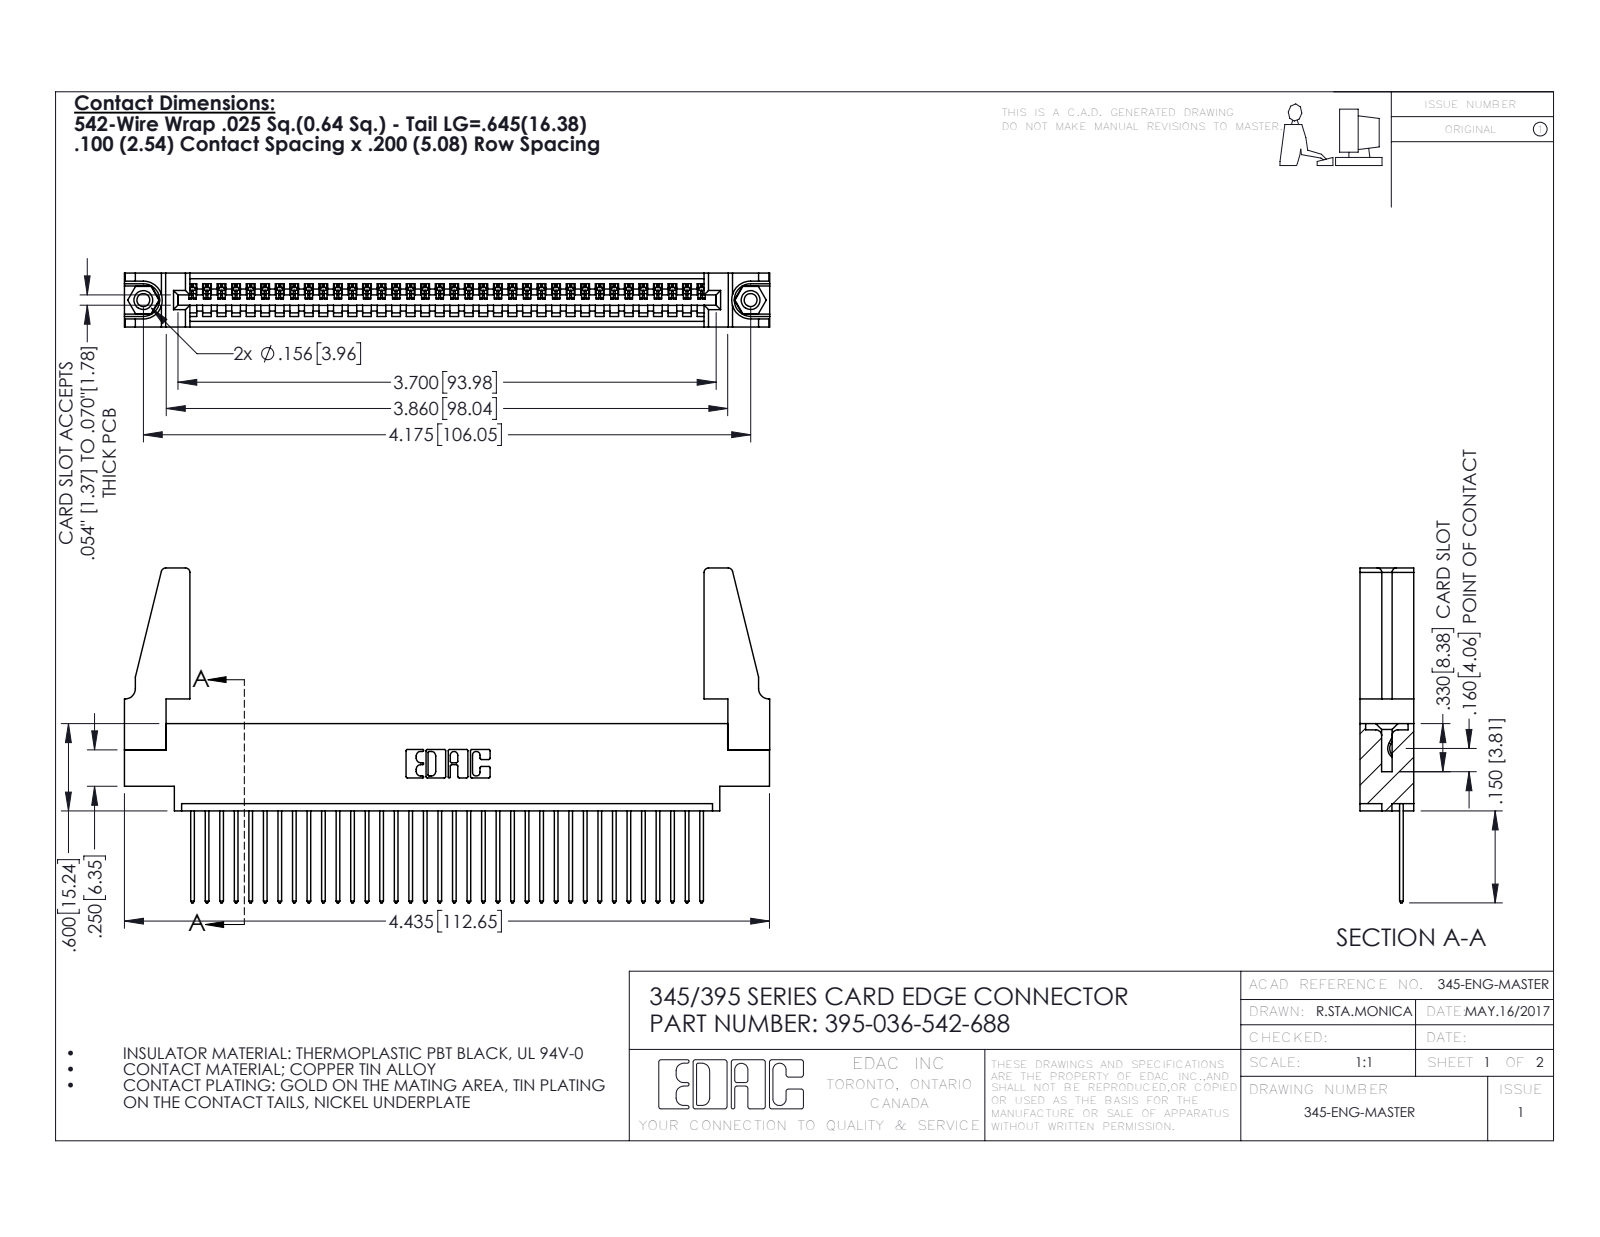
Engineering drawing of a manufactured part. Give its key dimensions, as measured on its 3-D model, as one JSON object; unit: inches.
{"part_name": "345-292-001_345-293-142; 345 Part_0.170 Offset - 0.156 Dia-TH; 395-036-542-688; 345-250-001_345-250-001-102 (+1 more)", "step_written_by": "SolidWorks 2016 (CONFIG_CONTROL_DESIGN)", "units": "inches", "bodies": {"solids": 41, "faces": 2342, "planar": 1596, "cylindrical": 730, "other": 16}, "overall_size": [4.436, 2.302, 0.37], "volume_in3": 0.847, "surface_area_in2": 27.58, "round_holes": [[0.089, 2], [0.125, 2], [0.156, 2], [0.064, 1]], "round_bosses_or_shafts": [[0.155, 2]], "partial_cylinders_radius": [[0.006, 72], [0.01, 72], [0.01, 22], [0.03, 8], [0.007, 6], [0.031, 6], [0.026, 3], [0.031, 2]], "face_to_face_distances": [0.072, 0.298, 0.37, 0.098, 0.272, 0.025, 0.2, 0.225, 0.175, 0.149], "hole_center_spacings": [0.27, 3.939, 4.175]}
